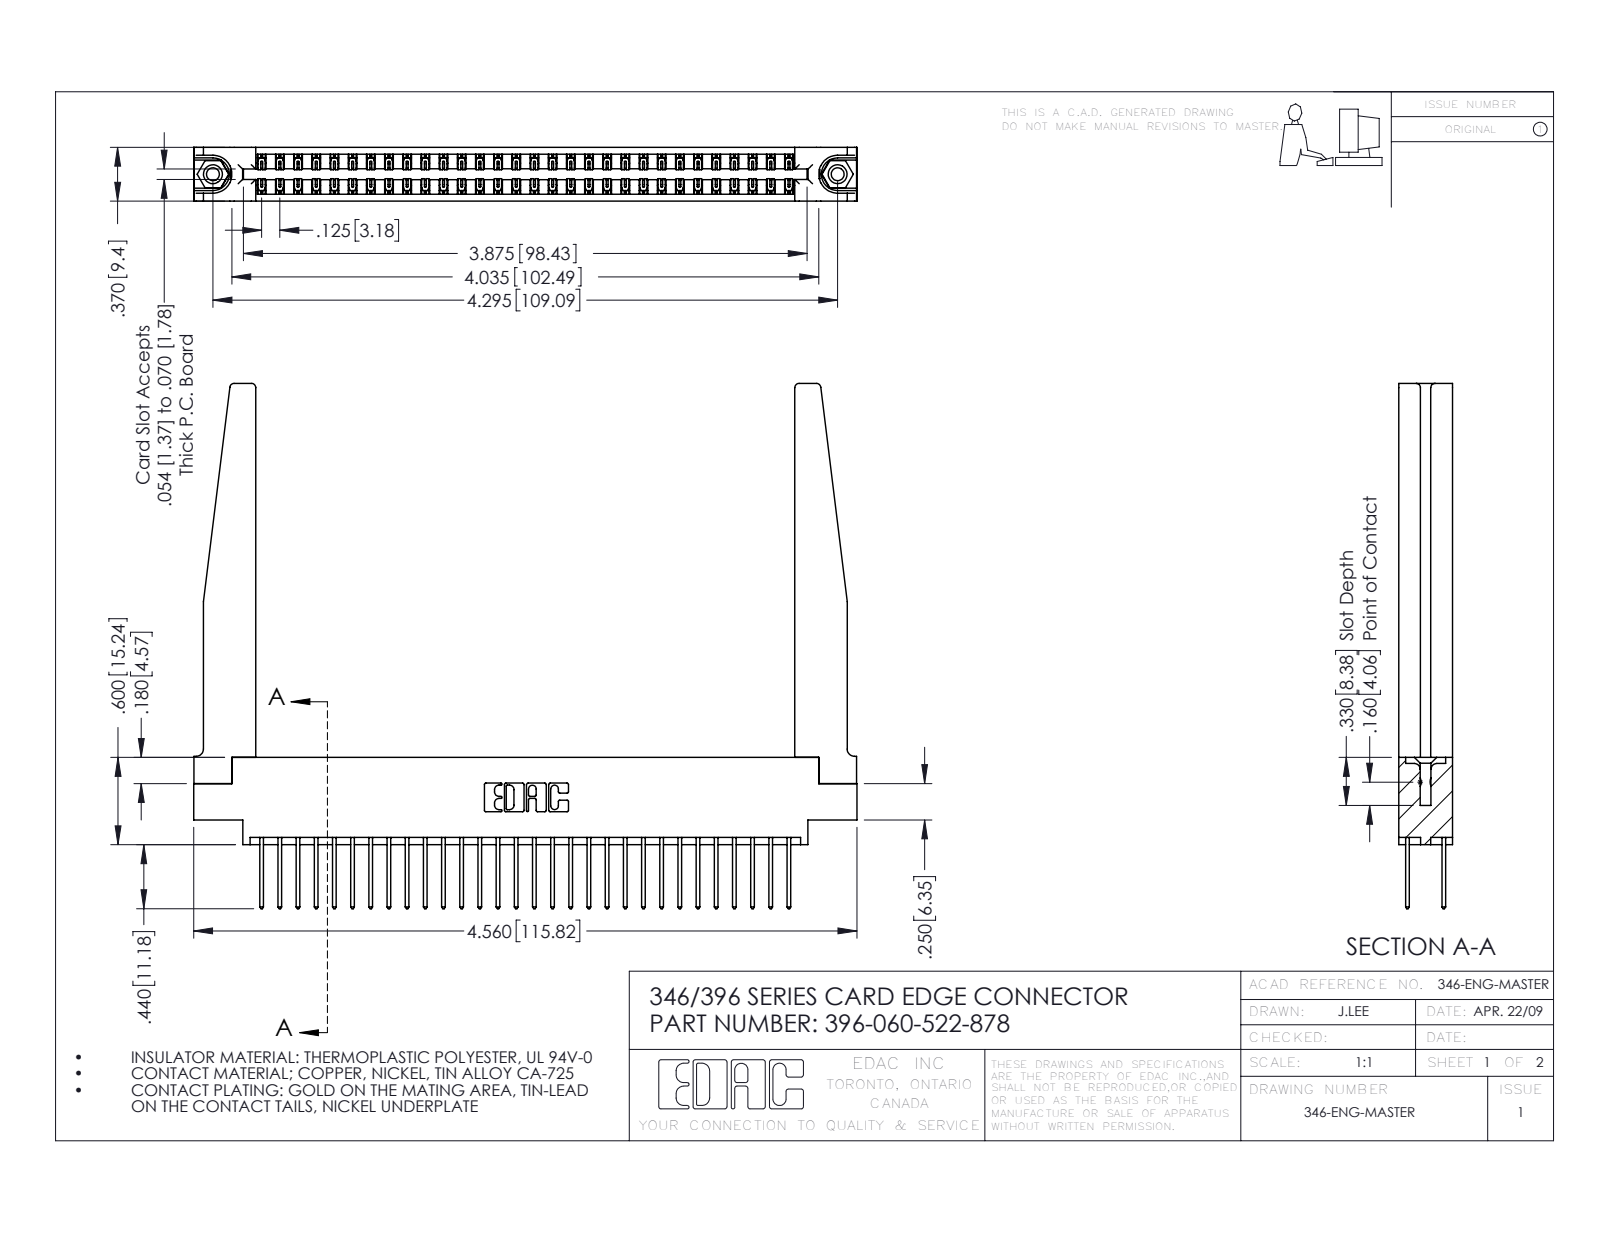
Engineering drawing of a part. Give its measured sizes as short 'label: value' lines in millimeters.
name: 346-220-078_345-220-078; 396-060-522-878; 346 Part_0.170 Offset - 0.156 Dia-TH; 345-292-001_345-293-122 (+1 more)
written by: SolidWorks 2016 (CONFIG_CONTROL_DESIGN)
unit: mm
bodies: 65 solids, 3480 faces (2322 planar, 1106 cylindrical, 52 other)
size: 115.8 × 91.7 × 9.4
volume: 18 110 mm³; area: 22 640 mm²
holes: 2× ⌀2.3, 2× ⌀3.2, 2× ⌀4, 1× ⌀1.6
bosses: 2× ⌀3.9
rounds: 90× R0.2, 60× R0.3, 22× R0.3, 8× R0.8, 6× R0.2, 6× R0.8, 3× R0.7, 2× R0.4
face distances: 9.4, 1.2, 8.2, 1.8, 6.4, 7.6, 0.6, 3.8, 3.8, 7
hole spacings: 6.2, 103.8, 109.1
